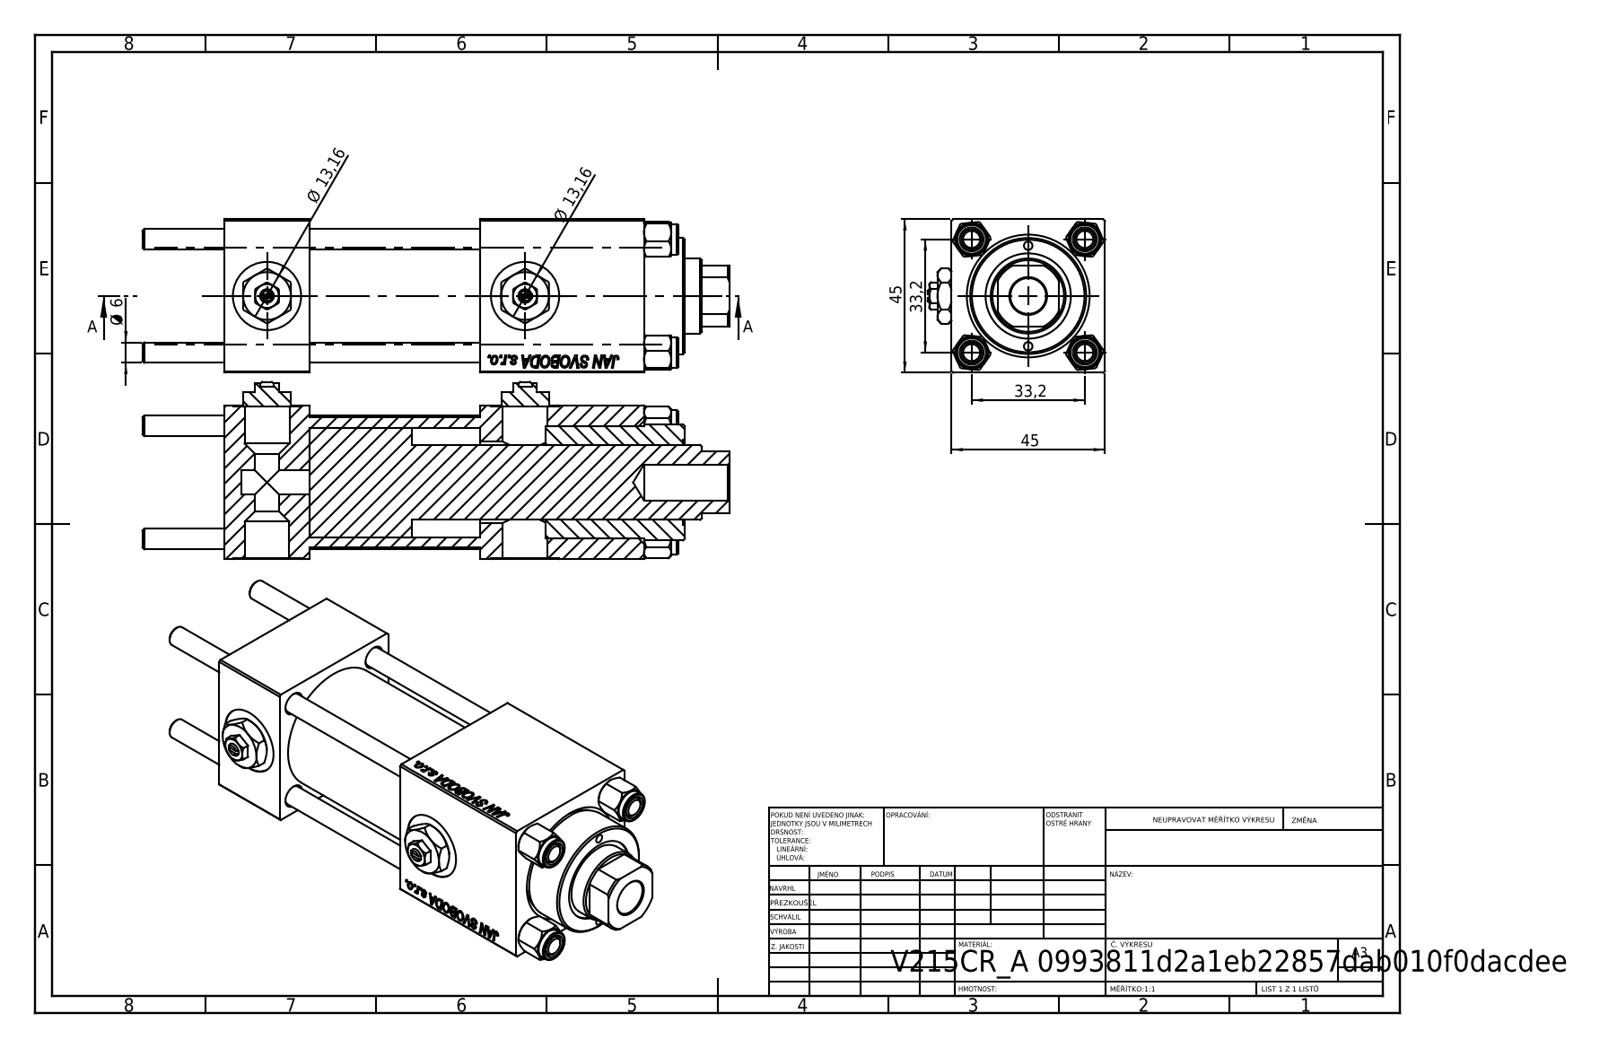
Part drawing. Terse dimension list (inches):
name: V215_VC_A; Zatka_pro_OIL_PORT; NUT_M5; V215CR_BODY_A (+2 more)
written by: SolidWorks 2019 (CONFIG_CONTROL_DESIGN)
unit: in
bodies: 13 solids, 1238 faces (566 planar, 94 cylindrical, 578 other)
size: 6.772 × 2.047 × 1.772
volume: 12.95 in³; area: 122.7 in²
holes: 4× ⌀0.236, 3× ⌀0.518, 3× ⌀0.787, 2× ⌀0.098, 2× ⌀0.276, 1× ⌀0.413, 1× ⌀0.512, 1× ⌀0.866, 1× ⌀0.945, 1× ⌀0.984, 1× ⌀1.26, 1× ⌀1.299
bosses: 4× ⌀0.354, 1× ⌀1.496, 1× ⌀1.339
rounds: 1× R0.413
face distances: 1.772, 0.984, 4.843, 1.969, 2.953, 3.858, 1.89, 1.764, 3.713, 2.728
hole spacings: 0.657, 0.924, 1.307, 1.396, 0.581, 1.848, 1.161, 2.972
